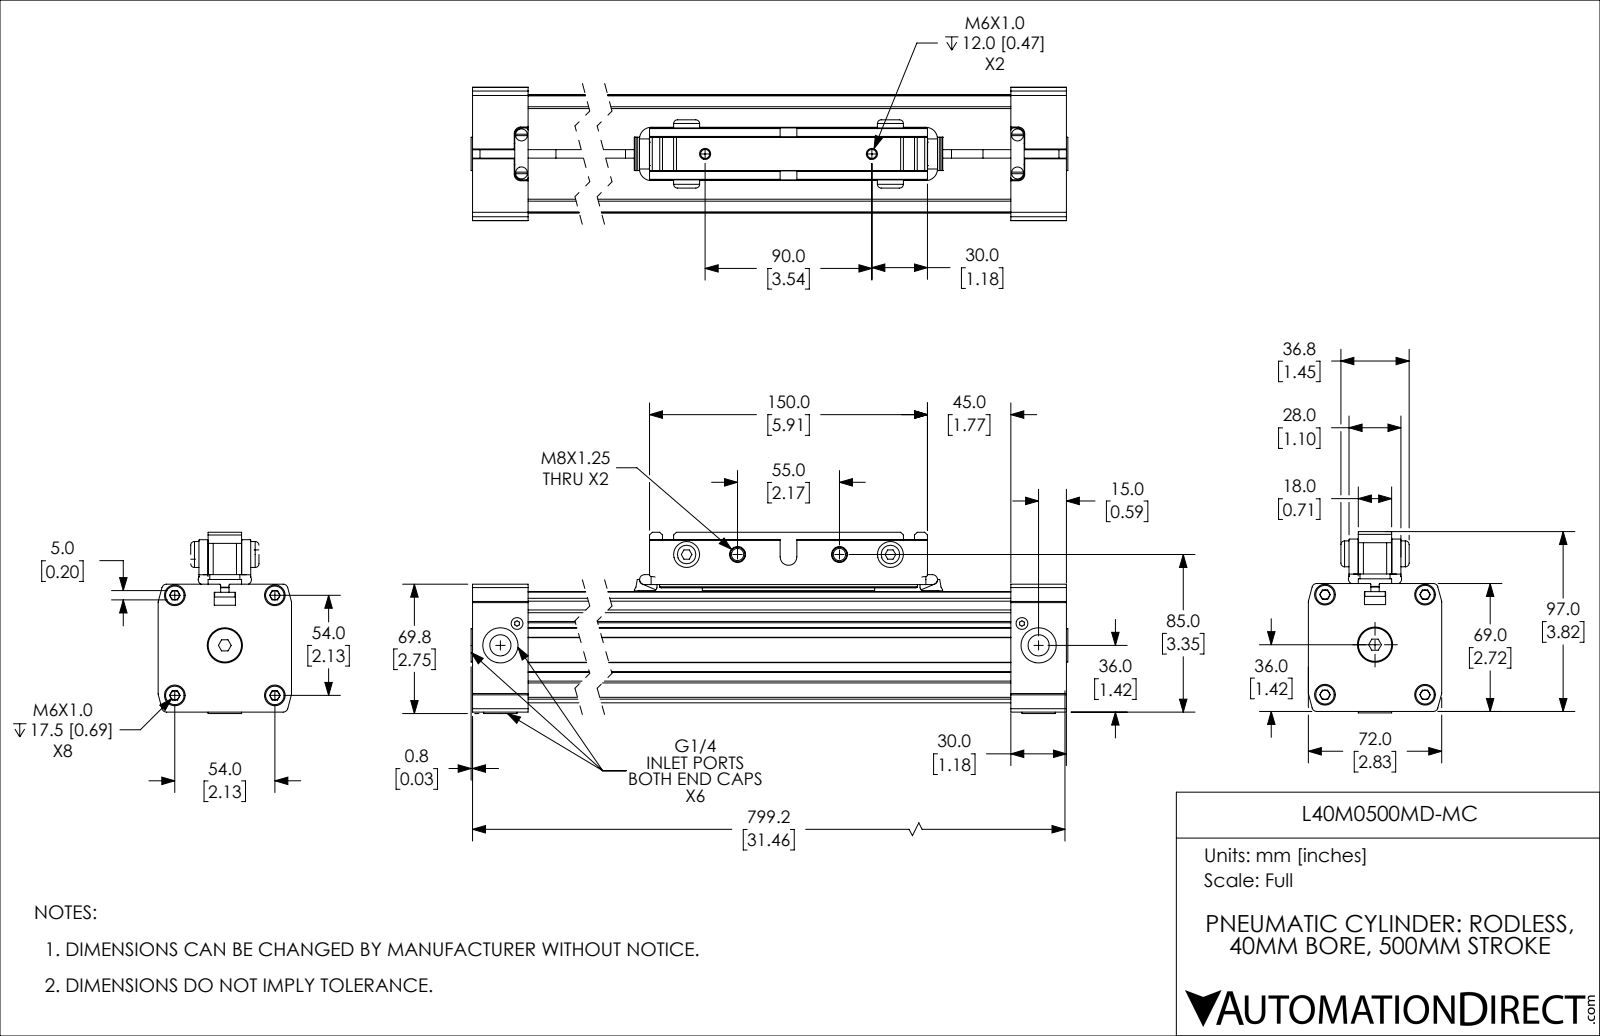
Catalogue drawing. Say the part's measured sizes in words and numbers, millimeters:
The part is named "L40M0500MD-MC_PISTON; L40M0500MD-MC; L40M0500MD-MC_BODY". Its 3-D file was written by "SolidWorks 2019 (CONFIG_CONTROL_DESIGN)". It is 13 solids with 821 faces: 451 planar, 278 cylindrical and 92 other. Overall it measures 801.6 by 97.8 by 72 millimeters. Its volume is 2 201 000 cubic millimeters and its surface area 463 900 square millimeters. Round holes: 6 of diameter 4.9, 5 of diameter 11.5, 5 of diameter 19, 4 of diameter 6.5, 4 of diameter 6.7, 4 of diameter 8.6, 4 of diameter 11.2, 2 of diameter 6.4, 1 of diameter 40.2. Round bosses or shafts: 4 of diameter 10, 4 of diameter 5.3, 3 of diameter 18, 3 of diameter 11.1, 2 of diameter 14, 2 of diameter 13.2, 1 of diameter 40, 1 of diameter 13.2. Partial cylindrical surfaces (rounded edges, fillets, slot ends): 30 of radius 1, 10 of radius 2, 8 of radius 0.3, 8 of radius 2.5, 8 of radius 3.5, 4 of radius 4, 2 of radius 0.2, 2 of radius 0.2. The main face-to-face distances are 60, 5.1, 63.6, 58.5, 18.6, 17.8, 30, 36.8, 0.8, 7. The hole center spacings are 15.3, 38.2, 54, 758.7, 14.8, 20.5, 27.5, 36.3.
